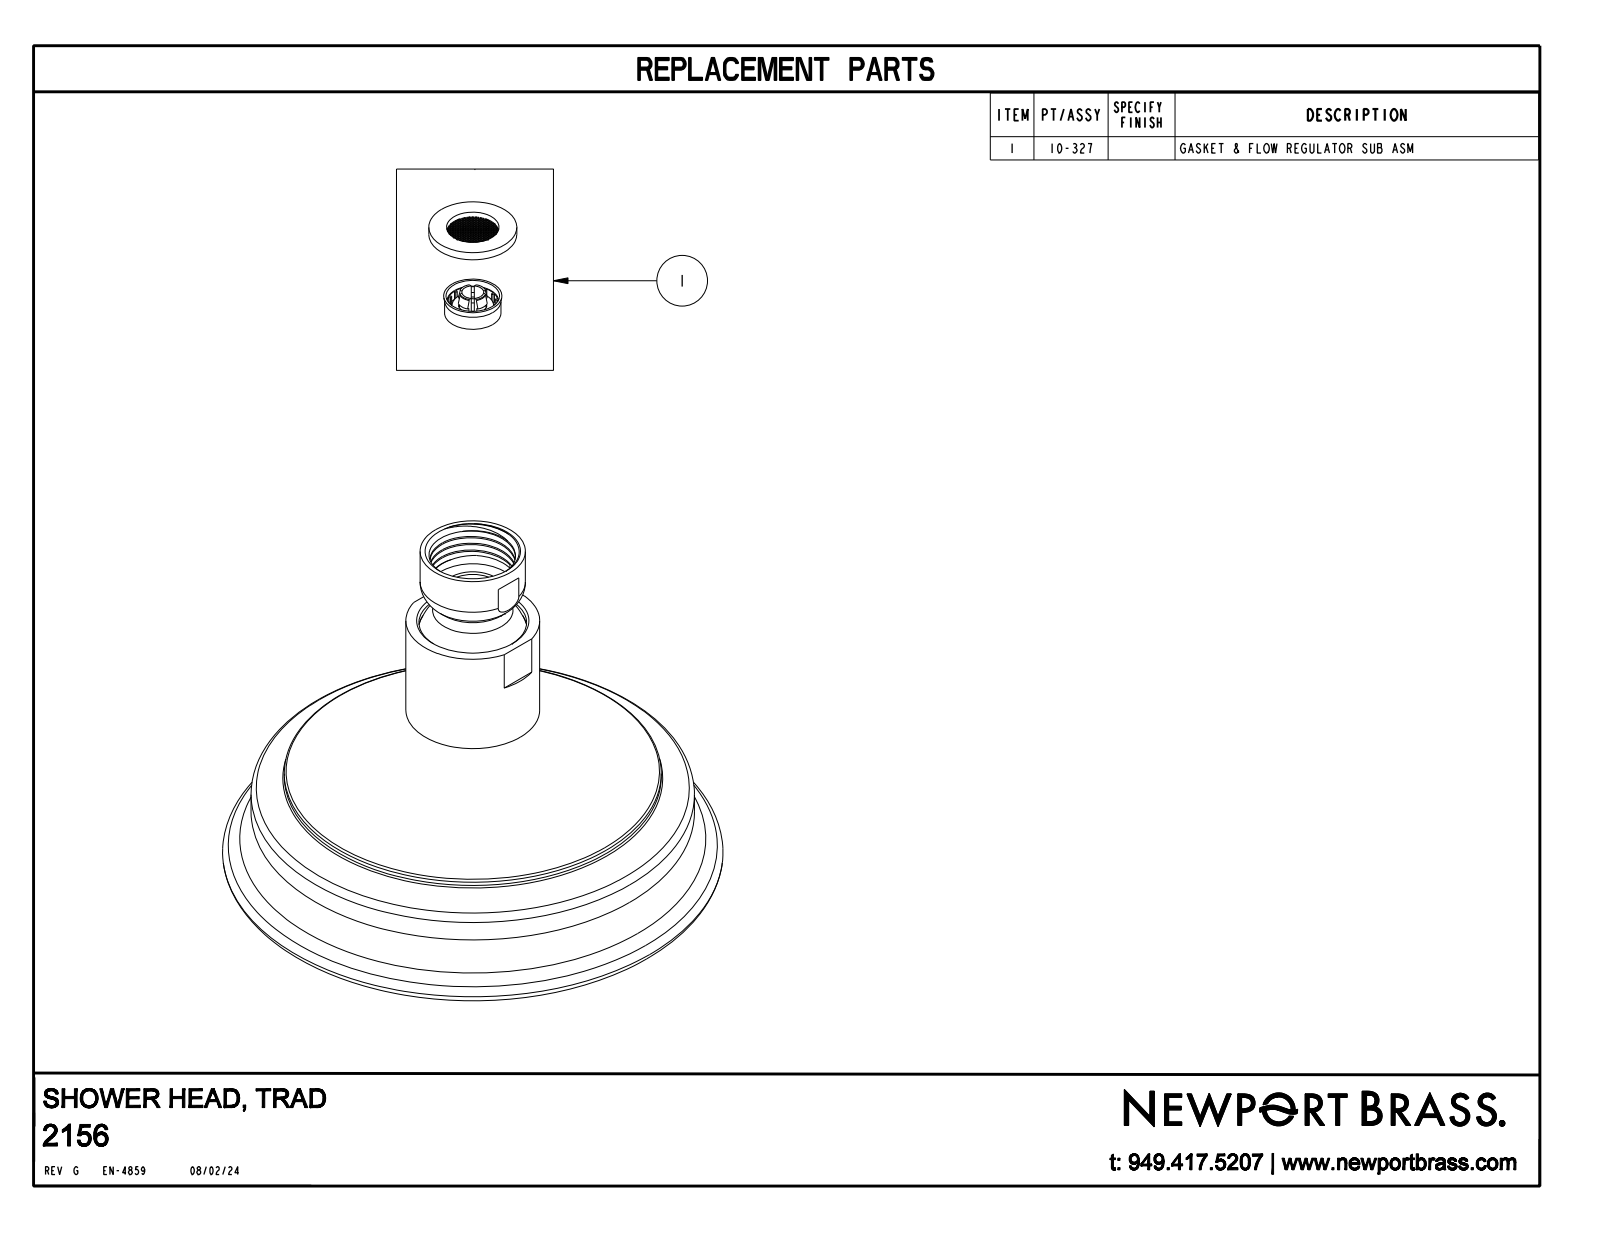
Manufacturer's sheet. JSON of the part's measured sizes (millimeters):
{"part_name": "80096; 8-083; 12113; 80018 (+1 more)", "step_written_by": "CREO PARAMETRIC BY PTC INC, 2018400 (AUTOMOTIVE_DESIGN)", "units": "millimeters", "bodies": {"solids": 29, "faces": 3760, "planar": 842, "cylindrical": 1063, "other": 1855}, "overall_size": [109.2, 109.2, 92.3], "volume_mm3": 162300, "surface_area_mm2": 162100, "round_holes": [[1.1, 32], [2.5, 15], [1.5, 12], [2, 8], [2.4, 8], [3, 7], [3.8, 3], [6.4, 3], [7, 3], [6.8, 2], [10, 2], [3.3, 1]], "round_bosses_or_shafts": [[3.6, 39], [4.2, 23], [8, 3], [6.2, 3], [5.8, 2], [96.8, 1], [94.6, 1], [93.4, 1]], "partial_cylinders_radius": [[0.5, 52], [0.3, 27], [2.1, 15], [2, 8], [2.2, 8], [18.9, 5], [20.1, 5], [1, 4]], "face_to_face_distances": [2.5, 5.3, 7.3, 7.8, 4.8, 2, 0.5, 2.7, 2.6, 2.8], "hole_center_spacings": [17.7, 4.4, 8.2, 9.6, 10.7, 11.1, 15.1, 16.7]}
